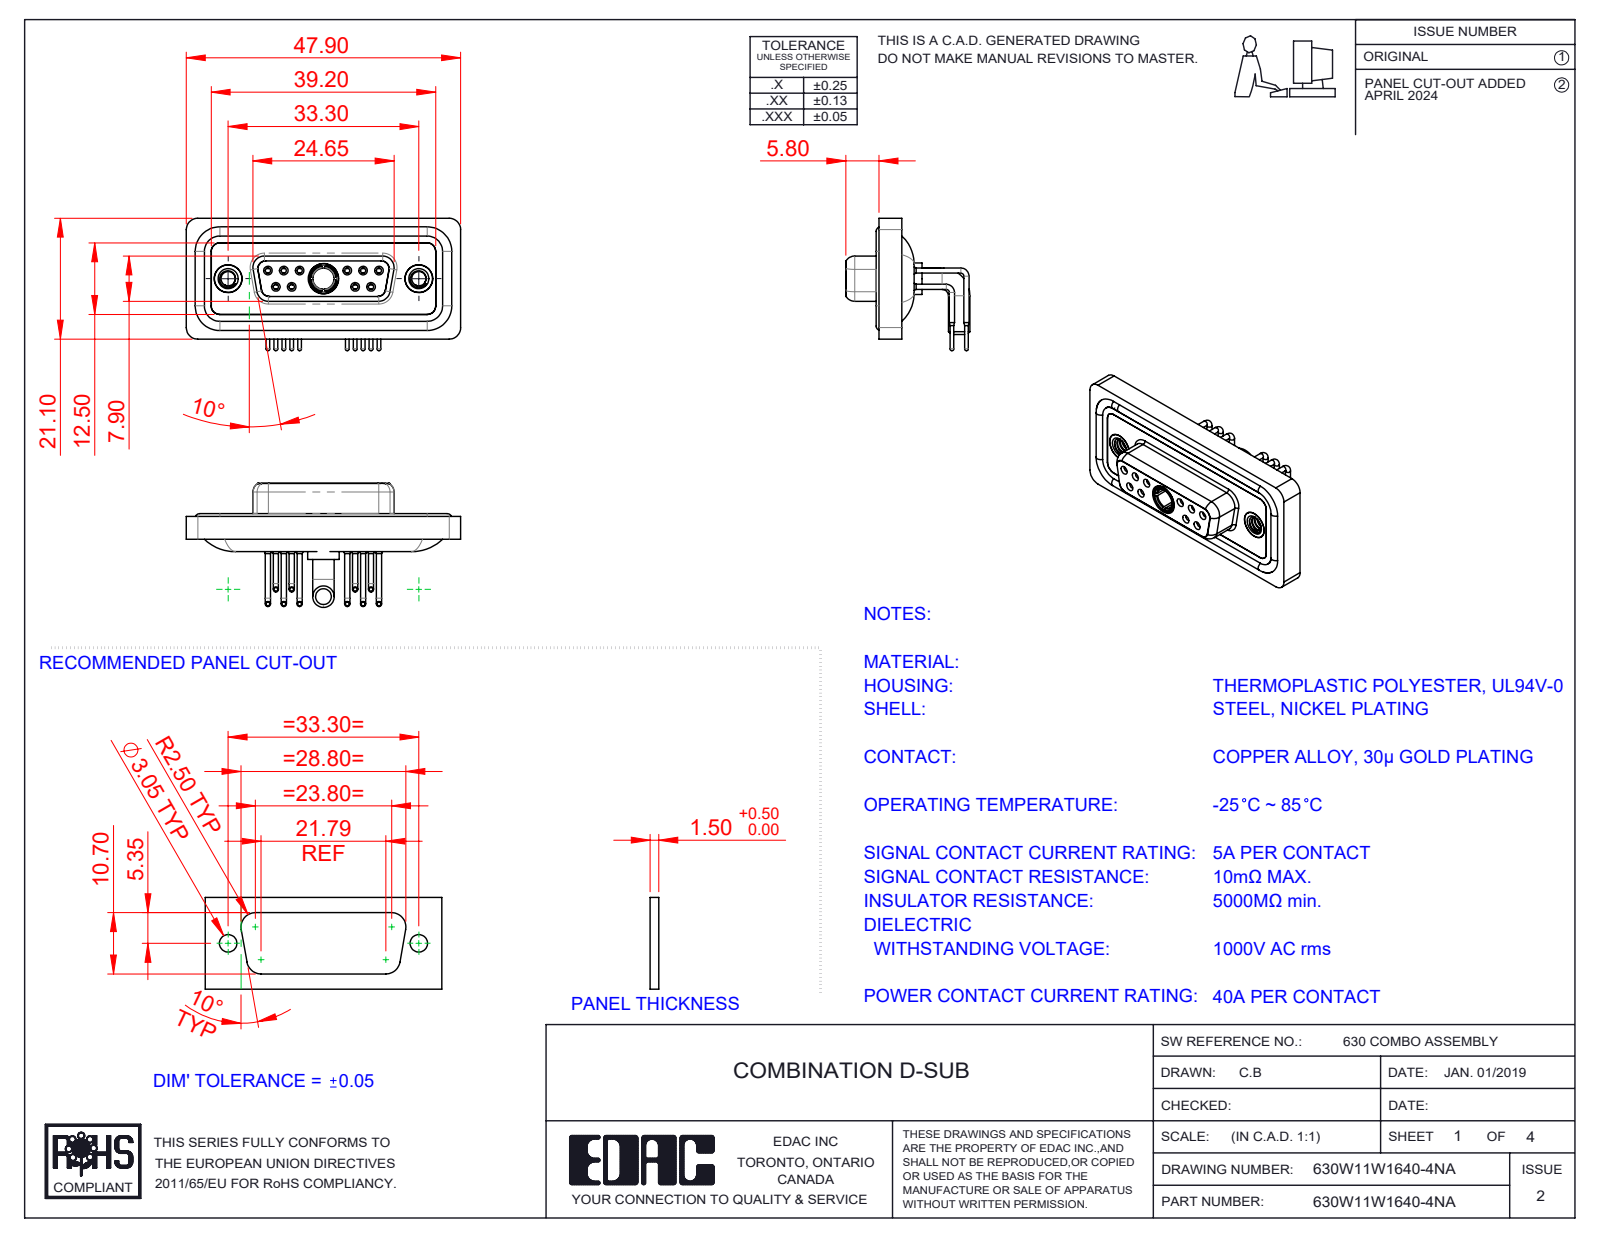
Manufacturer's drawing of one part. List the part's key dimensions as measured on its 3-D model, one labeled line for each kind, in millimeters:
Part name (STEP PRODUCT): 630Combo Shell Front_15 Contacts; Power Socket_40A RA; 630Combo Waterproof Housing_15 Contacts; 630Combo Contact Row 1_50 Contacts (+5 more)
STEP written by: SolidWorks 2023 (CONFIG_CONTROL_DESIGN)
Units: millimetres
Bodies: 19 solids, 988 faces (284 planar, 441 cylindrical, 263 other)
Overall size (bounding box): 47.9 × 23.12 × 21.68
Volume: 6 283 mm³ · Surface area: 10 518 mm²
Round holes (diameter × count): ⌀0.9 ×10, ⌀1.1 ×10, ⌀1.5 ×10, ⌀2 ×10, ⌀1.7 ×6, ⌀1.6 ×4, ⌀4.85 ×3, ⌀2.5 ×2, ⌀4 ×2, ⌀4.05 ×2, ⌀5 ×2, ⌀3.7 ×1
Round bosses / shafts (diameter × count): ⌀1.6 ×10, ⌀0.9 ×10, ⌀0.65 ×10, ⌀4.95 ×2, ⌀4.8 ×2, ⌀3.75 ×2, ⌀5.5 ×1, ⌀5.2 ×1
Partial cylindrical surfaces — rounded edges, fillets, slot ends (radius × count): R2 ×20, R1.5 ×18, R1.35 ×12, R1.6 ×8, R0.25 ×4, R0.5 ×4, R0.6 ×4, R0.65 ×4
Main face-to-face distances: 0.4, 1.8, 1.1, 1.6, 2.5, 2.9, 3.1, 3.7, 4.1, 1.5
Hole centre spacings: 3.16, 2.77, 13.85, 11.08, 16.62, 5.03, 5.04, 5.54
